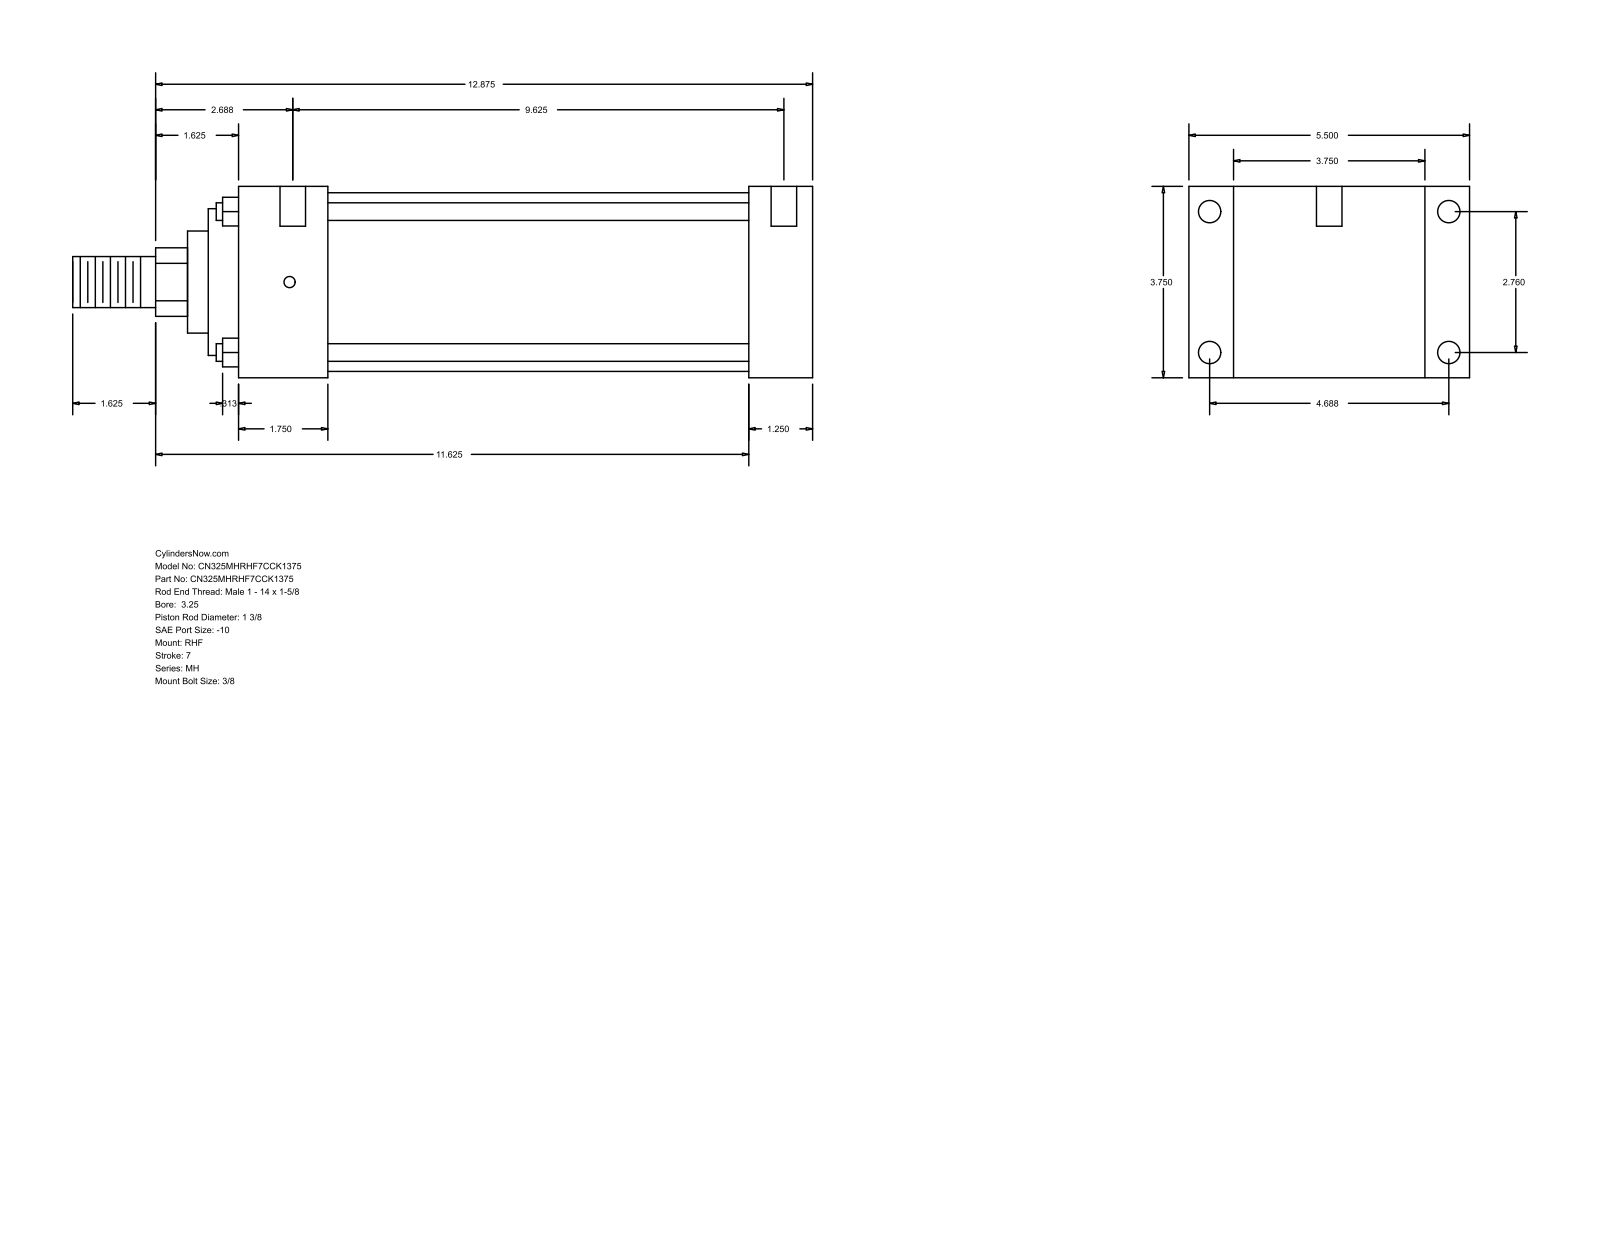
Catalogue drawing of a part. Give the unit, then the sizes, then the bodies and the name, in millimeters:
Units: millimetres
Overall size (bounding box): 368.3 × 139.7 × 95.25
Round holes (diameter × count): ⌀5.56 ×4, ⌀11.13 ×4, ⌀12.7 ×2
Round bosses / shafts (diameter × count): ⌀8.76 ×4, ⌀88.9 ×1, ⌀73.03 ×1, ⌀50.8 ×1, ⌀34.92 ×1, ⌀25.4 ×1
Partial cylindrical surfaces — rounded edges, fillets, slot ends (radius × count): R17.06 ×1
Main face-to-face distances: 95.24, 31.75, 22.23, 117.47, 254, 285.75, 139.7, 44.45, 209.55, 241.3
Hole centre spacings: 70.1, 119.06, 138.16, 250.83, 1.59, 4.76, 244.48, 246.07
Bodies: 0 solids, 90 faces (61 planar, 29 cylindrical, 0 other)
Part name (STEP PRODUCT): MH_RHF__0325_1.375
STEP written by: GSSL Pune (CONFIG_CONTROL_DESIGN)
